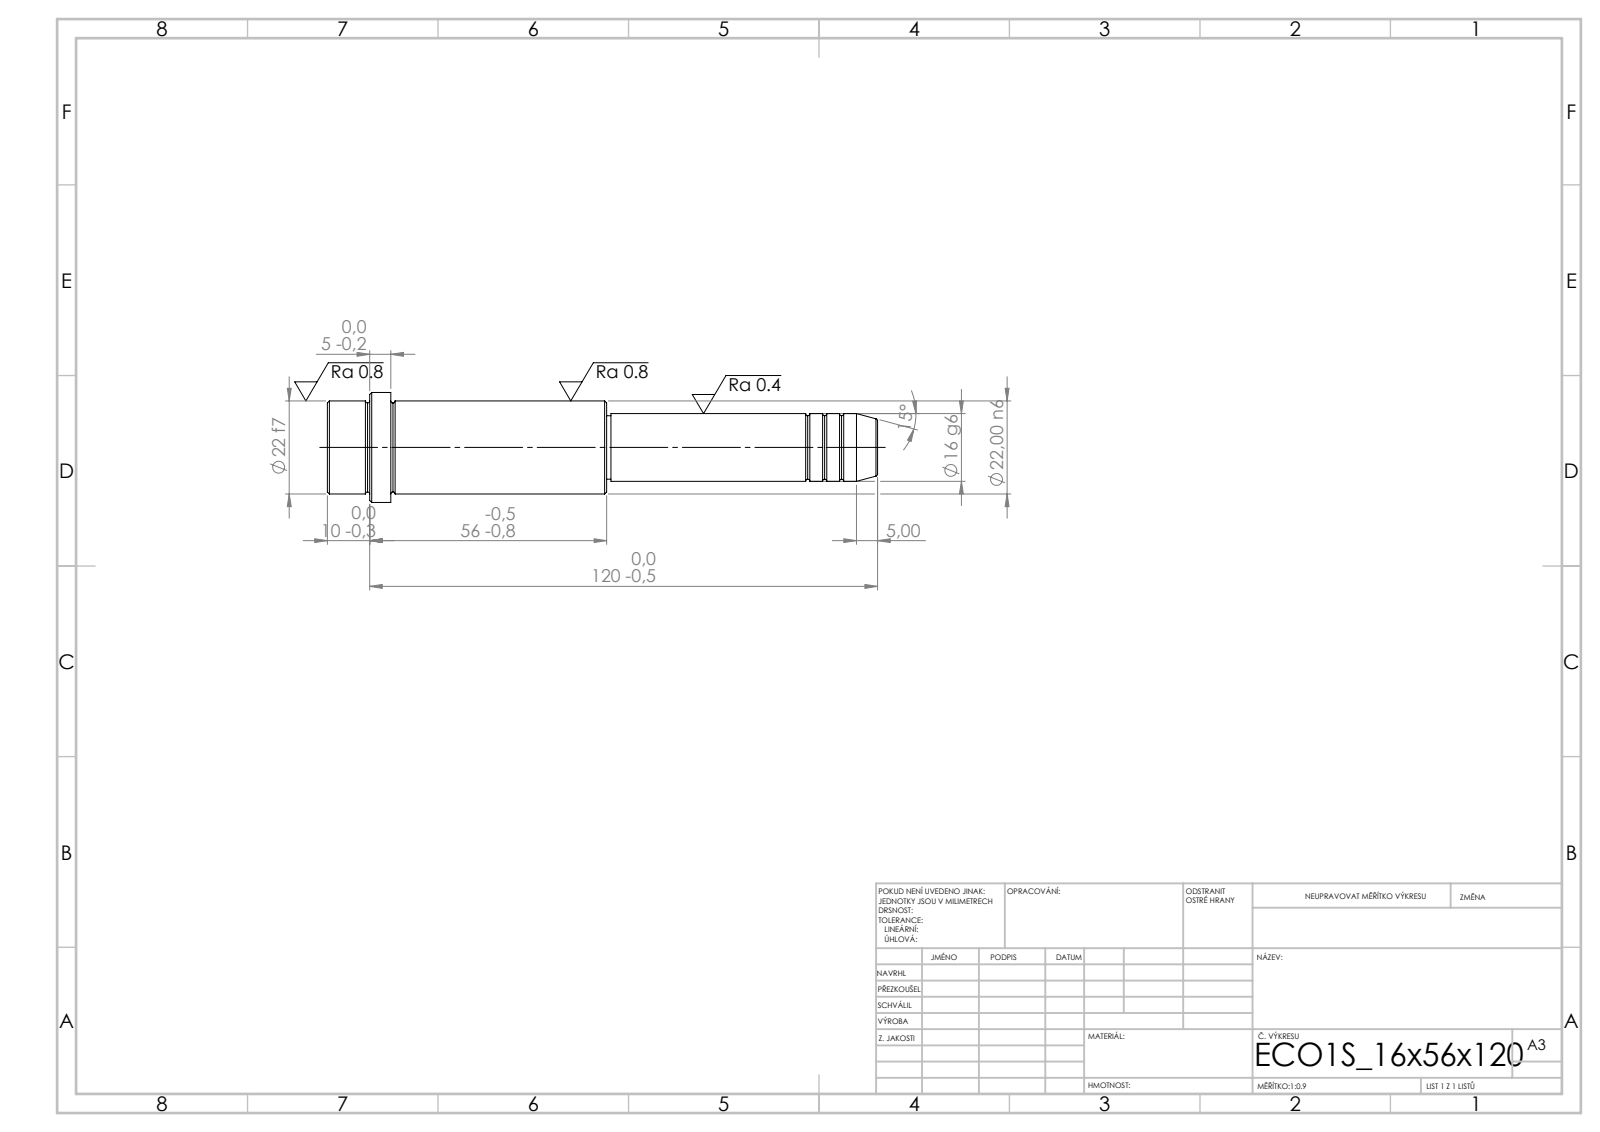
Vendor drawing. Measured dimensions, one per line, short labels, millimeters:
written by: SolidWorks 2019 (CONFIG_CONTROL_DESIGN)
unit: mm
bodies: 1 solid, 52 faces (6 planar, 16 cylindrical, 30 other)
size: 130 × 26 × 26
volume: 38 388 mm³; area: 8 953 mm²
bosses: 1× ⌀26, 1× ⌀22, 1× ⌀16, 1× ⌀15
face distances: 66, 51, 15, 64, 115, 130, 120, 56, 5, 10
